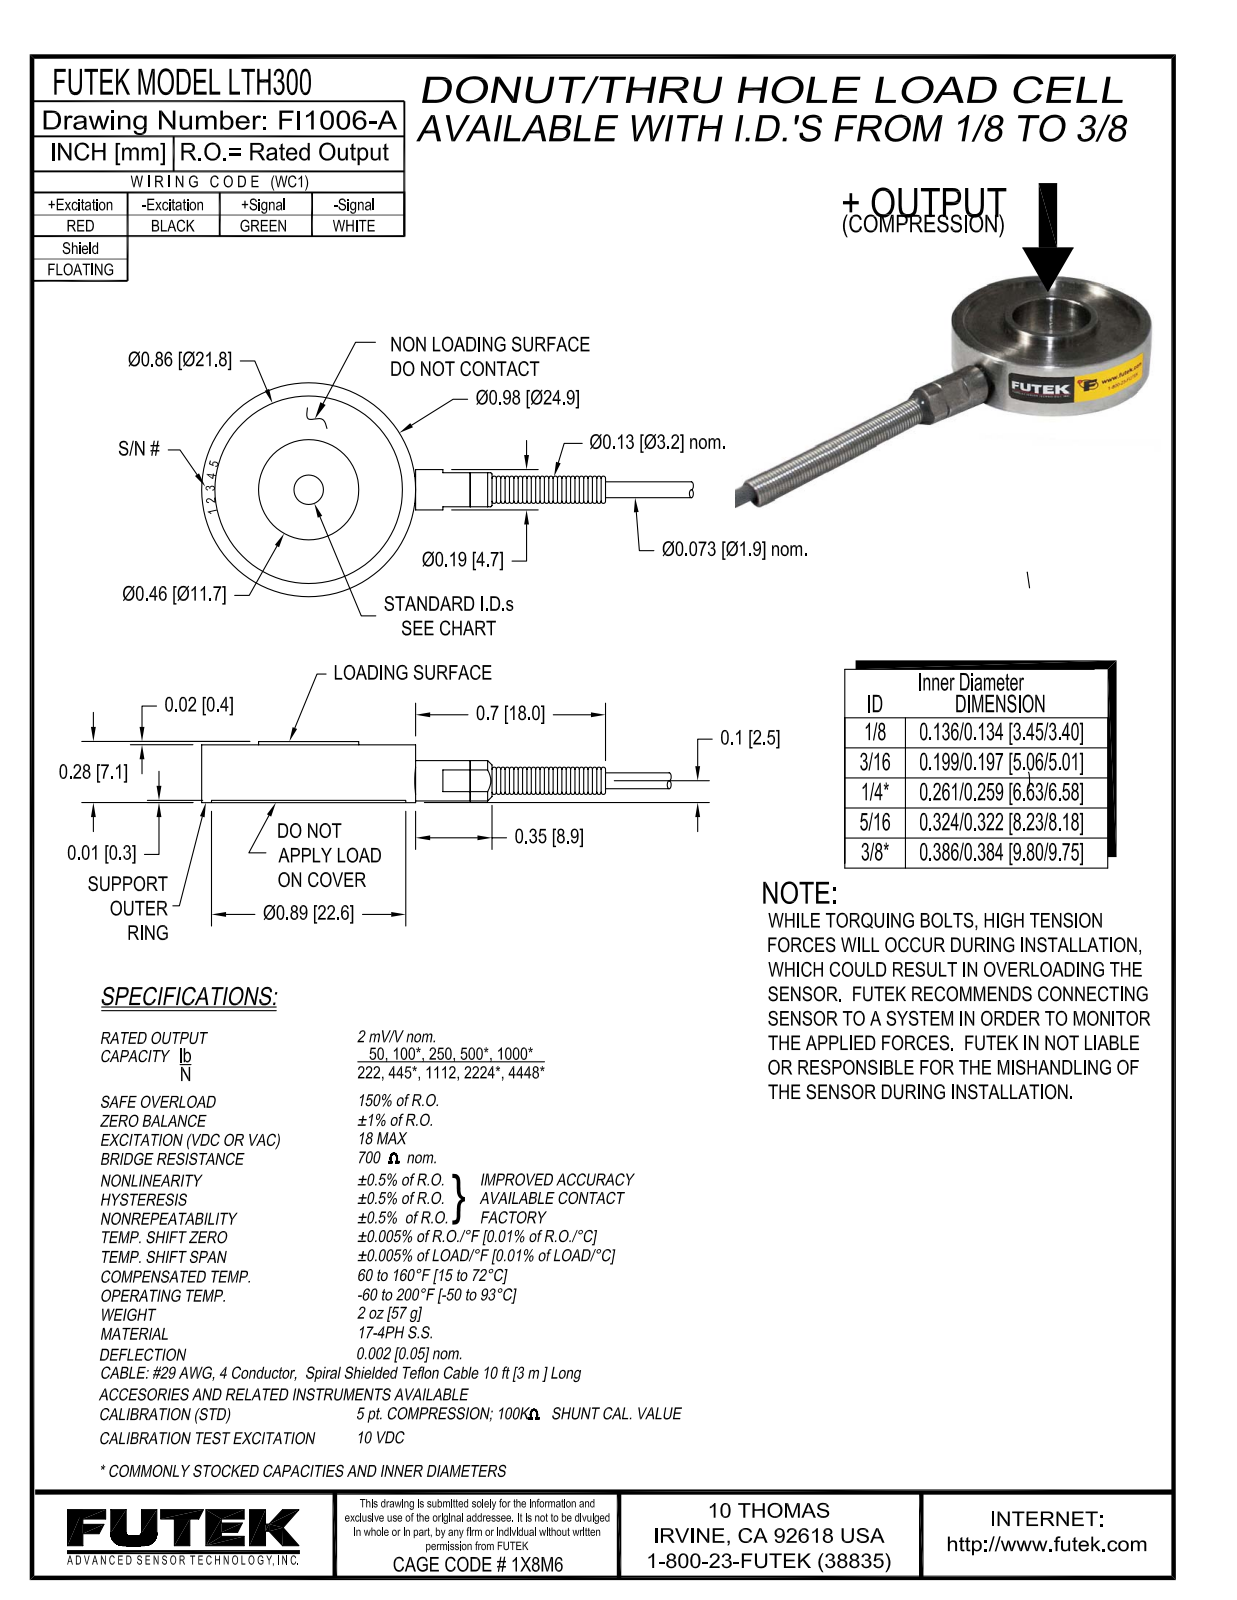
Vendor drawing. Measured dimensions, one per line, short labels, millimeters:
name: 5-16 ID; ~PART1
written by: Autodesk Inventor 2008 (AUTOMOTIVE_DESIGN)
unit: mm
bodies: 1 solid, 95 faces (34 planar, 23 cylindrical, 38 other)
size: 96.3 × 24.9 × 7.1
volume: 3 020 mm³; area: 2 508 mm²
holes: 1× ⌀2.1, 1× ⌀3, 1× ⌀3, 1× ⌀8.2, 1× ⌀11.3, 1× ⌀21.8, 1× ⌀22.4, 1× ⌀22.6
bosses: 3× ⌀1.9, 1× ⌀24.9, 1× ⌀22.3, 1× ⌀11.7, 1× ⌀11.2, 1× ⌀4.7, 1× ⌀3.2, 1× ⌀2.8
face distances: 5.8, 6.5, 0.6, 6.1, 6.7, 6.9, 7.1, 1, 0.4, 0.5
